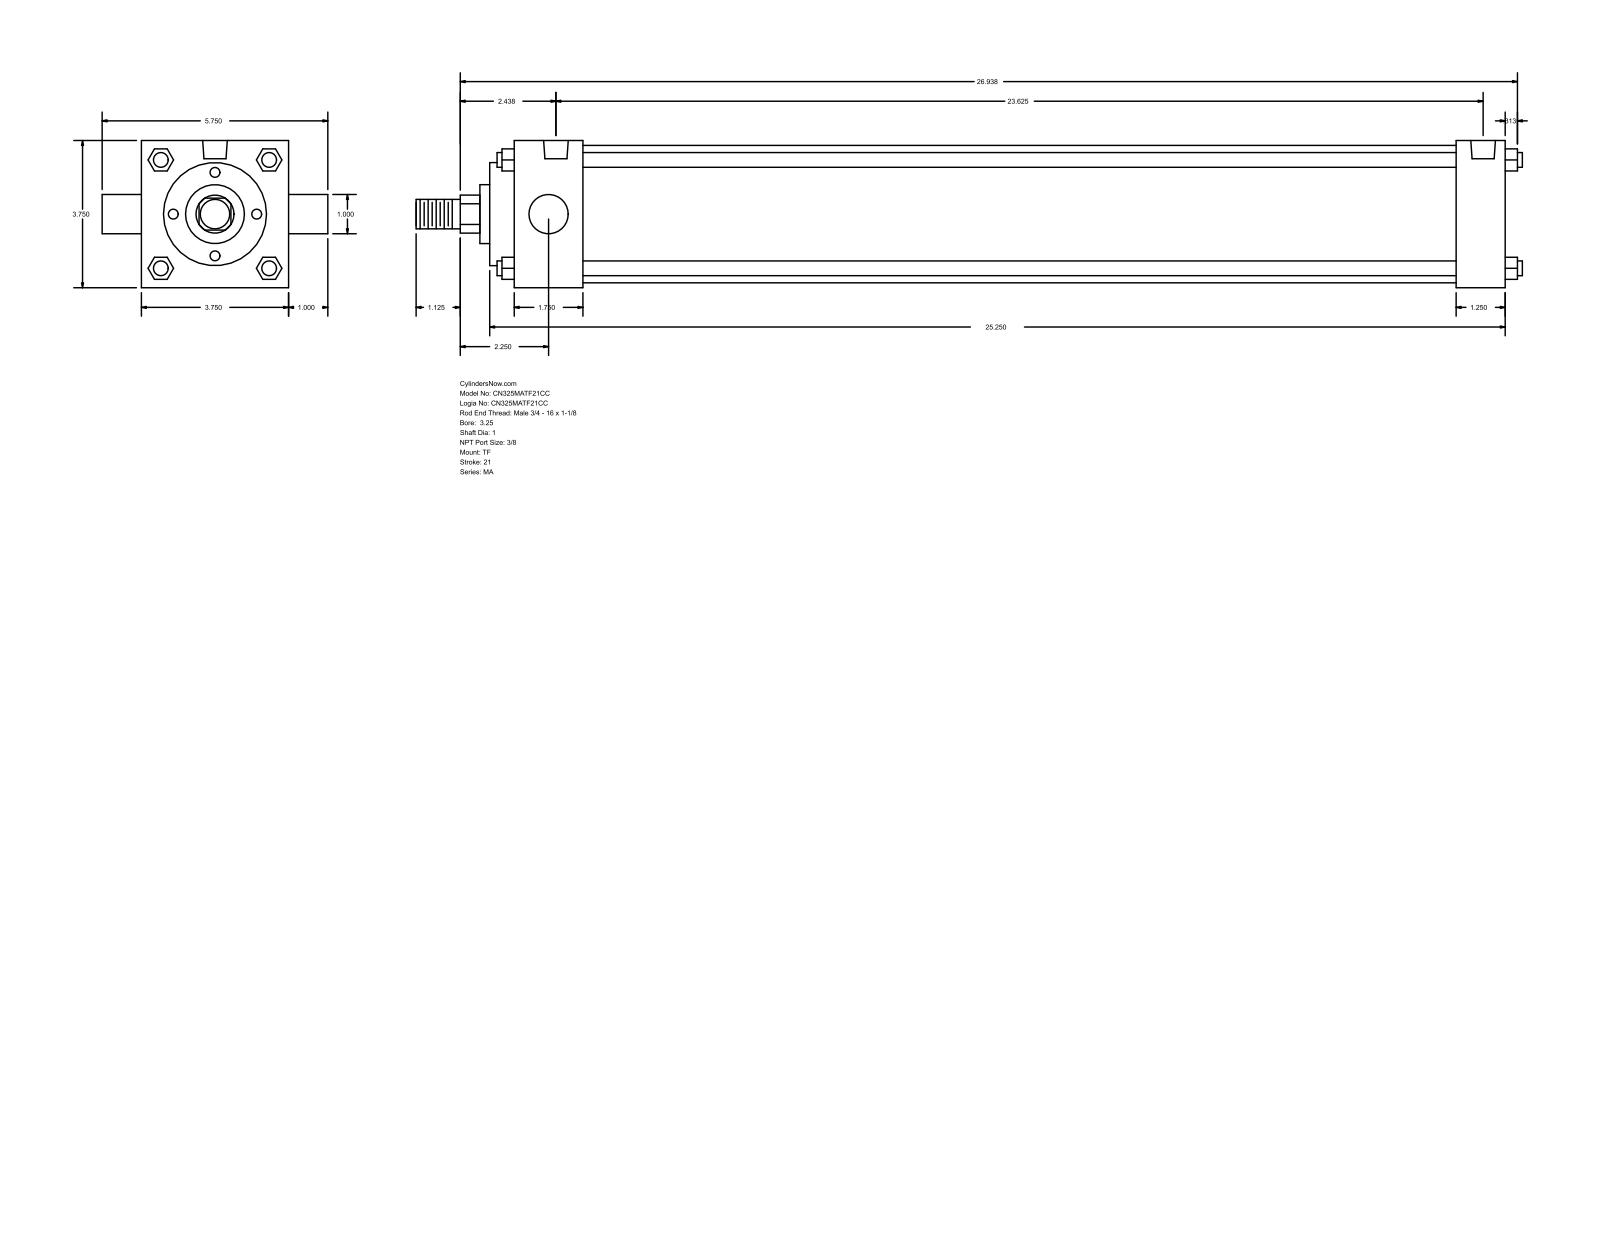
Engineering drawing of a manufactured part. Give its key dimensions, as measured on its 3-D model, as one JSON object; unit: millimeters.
{"part_name": "MA_TF__0325_1", "step_written_by": "GSSL Pune (CONFIG_CONTROL_DESIGN)", "units": "millimeters", "bodies": {"solids": 0, "faces": 122, "planar": 93, "cylindrical": 29, "other": 0}, "overall_size": [715.96, 146.05, 95.25], "round_holes": [[11.11, 3], [15.93, 2]], "round_bosses_or_shafts": [[9.53, 4], [25.4, 2], [88.9, 1], [66.67, 1], [38.1, 1], [19.05, 1]], "partial_cylinders_radius": [[12.29, 1]], "face_to_face_distances": [95.24, 641.35, 657.22, 44.46, 609.6, 565.14, 596.89, 31.75, 15.87, 60.33], "hole_center_spacings": [4.76, 595.32, 590.56, 600.08]}
